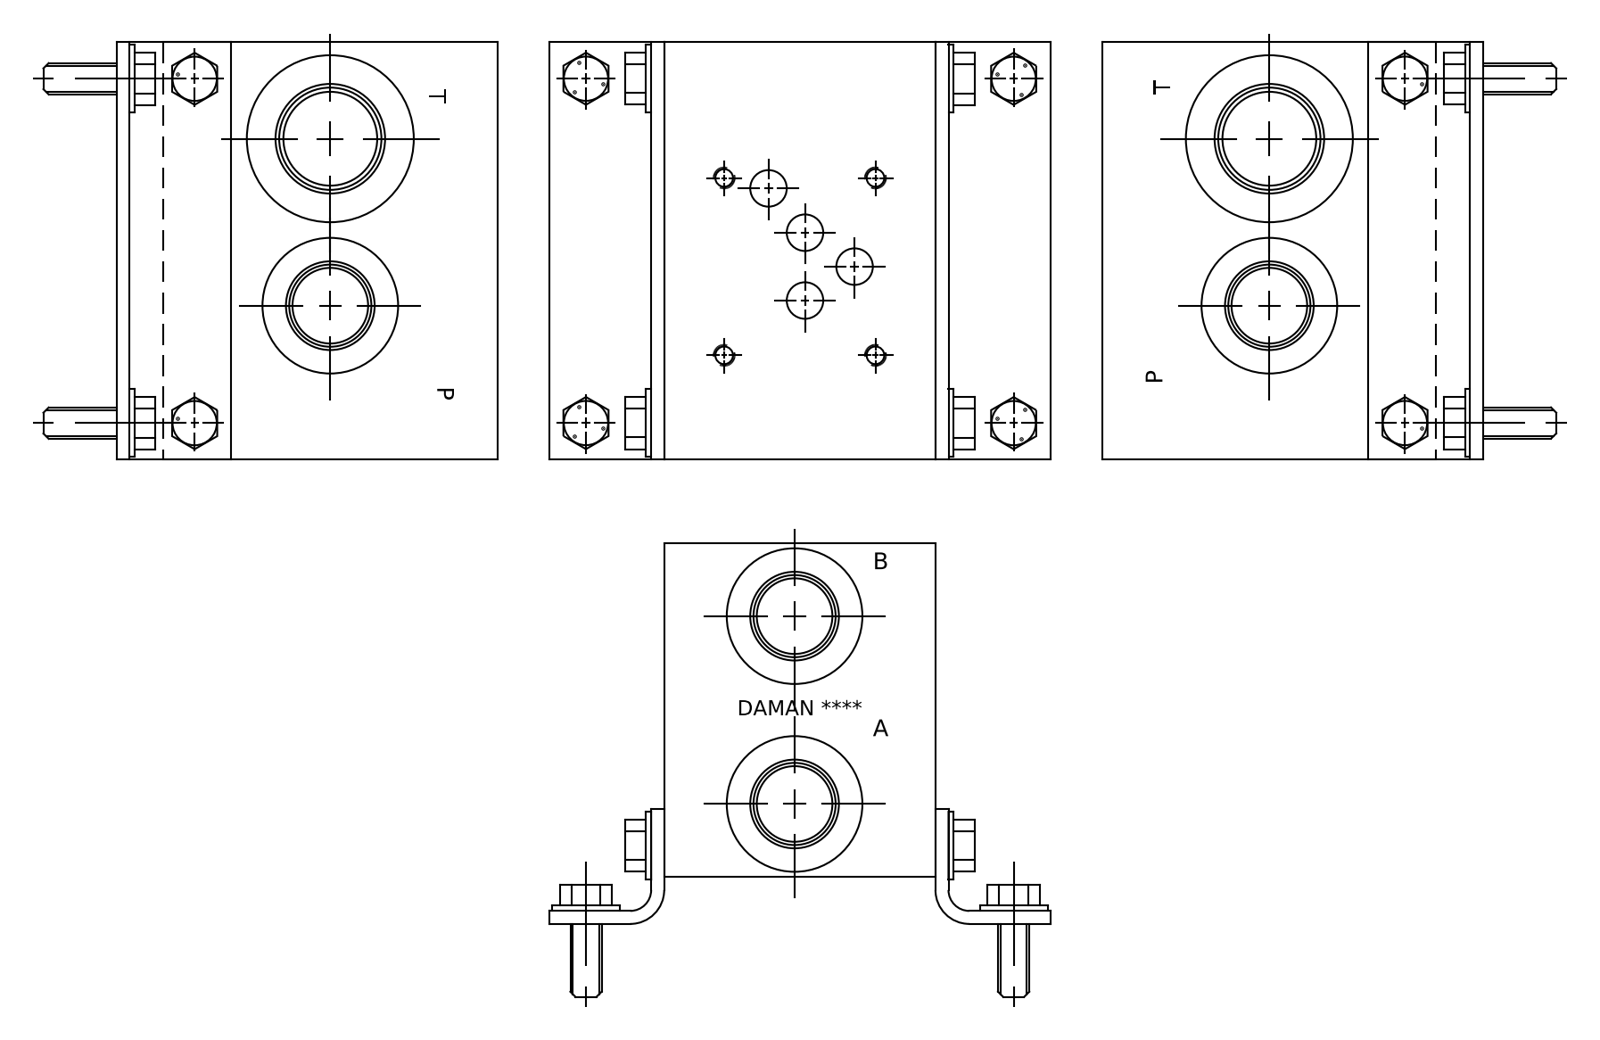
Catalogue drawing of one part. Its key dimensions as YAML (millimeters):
part_name: "Part_DD05HP013S_3D"
step_written_by: "Autodesk Inventor 2019 (AUTOMOTIVE_DESIGN)"
units: millimeters
bodies: {solids: 1, faces: 528, planar: 312, cylindrical: 51, other: 165}
overall_size: [127, 101.6, 82.55]
volume: 923407
surface_area: 85858
round_holes:
  - {diameter: 5.11, count: 4}
  - {diameter: 6.35, count: 4}
  - {diameter: 23.01, count: 3}
  - {diameter: 24.92, count: 3}
  - {diameter: 27.43, count: 3}
  - {diameter: 42.04, count: 3}
  - {diameter: 7.92, count: 2}
  - {diameter: 9.53, count: 2}
  - {diameter: 11.11, count: 2}
  - {diameter: 11.13, count: 2}
  - {diameter: 26.99, count: 2}
  - {diameter: 27, count: 2}
face_to_face_distances: [101.6, 82.55, 127, 0.79, 81.76, 80.97, 126.21, 19.05, 19.84, 62.71]
hole_center_spacings: [18.28, 29.74, 46.05, 70.95, 13.88, 17.49, 20.63, 27.13]
